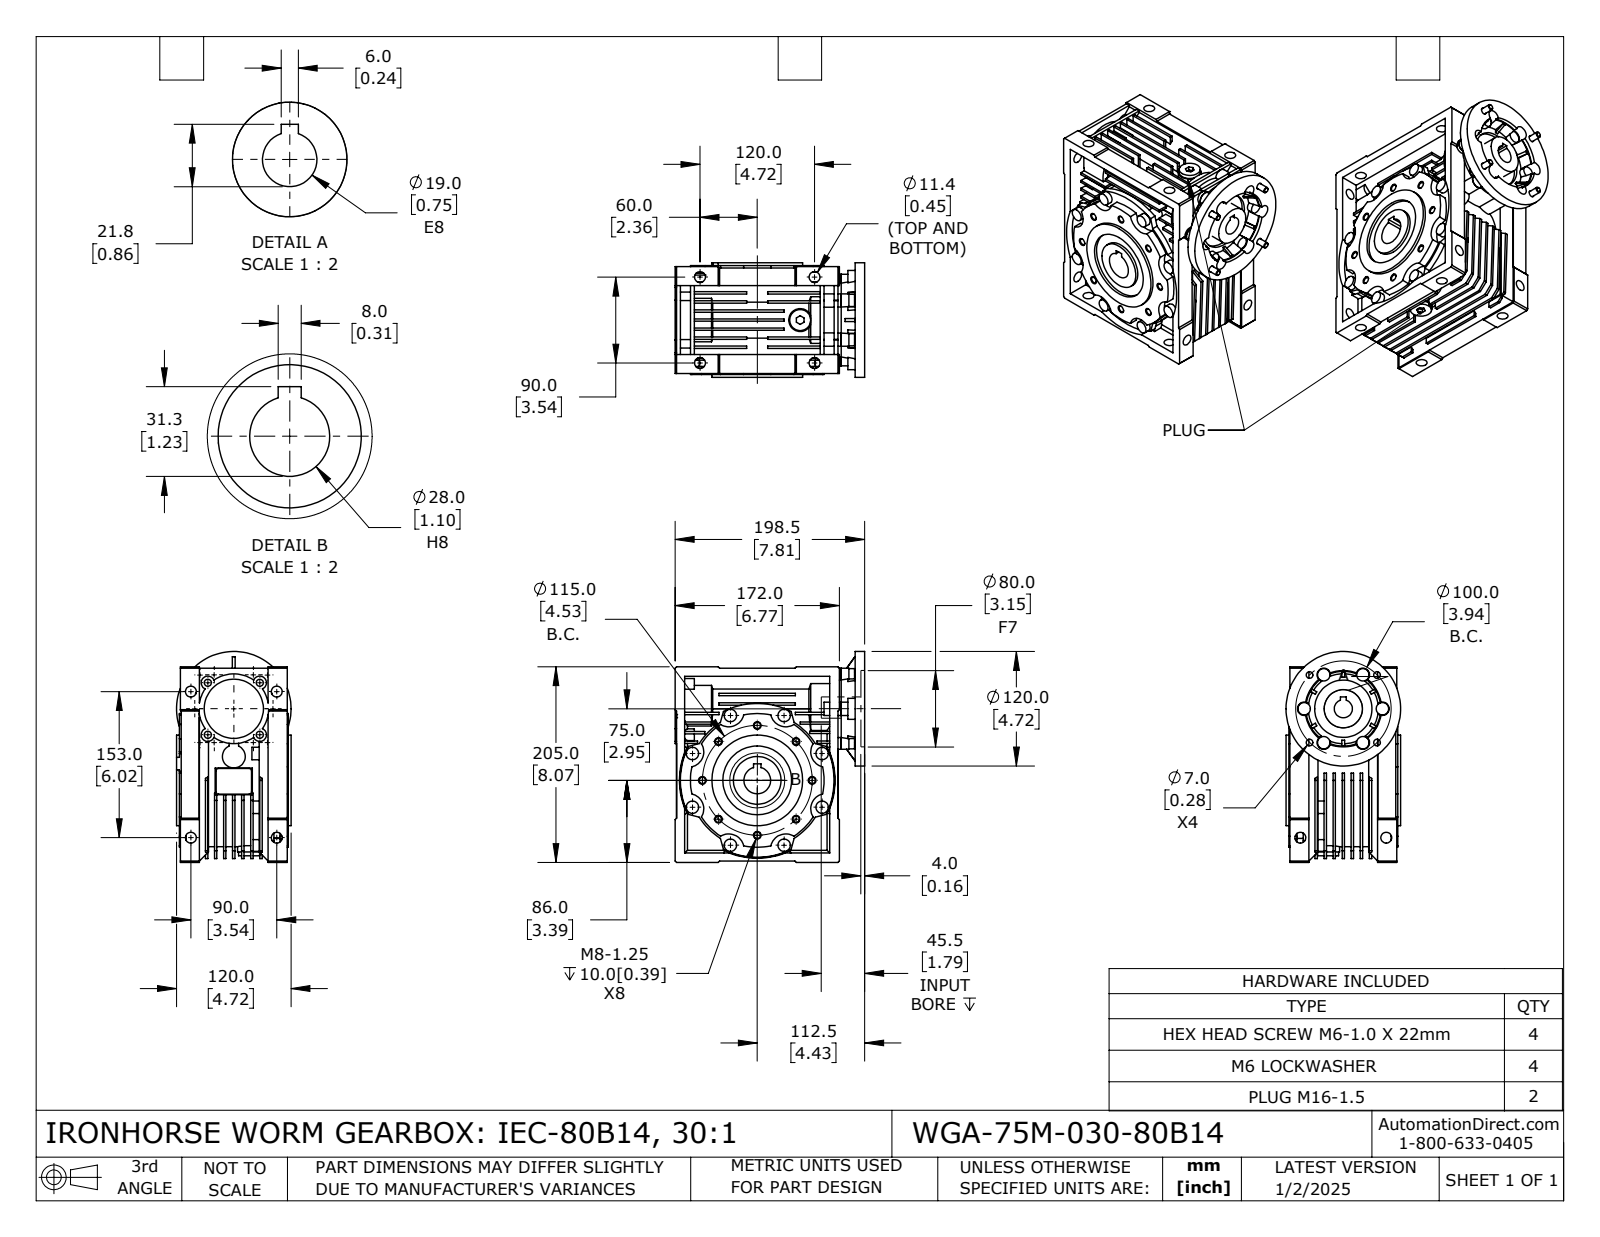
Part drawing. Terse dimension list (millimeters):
name: WGA-75M-030-80B14
written by: SolidWorks 2024 (CONFIG_CONTROL_DESIGN)
unit: mm
bodies: 16 solids, 1304 faces (703 planar, 433 cylindrical, 168 other)
size: 221 × 209 × 120
volume: 2 853 000 mm³; area: 480 911 mm²
holes: 8× ⌀6.65, 8× ⌀11.38, 4× ⌀6.1, 4× ⌀7, 4× ⌀7.45, 2× ⌀14.5, 1× ⌀19, 1× ⌀20, 1× ⌀28, 1× ⌀39, 1× ⌀42, 1× ⌀50
bosses: 14× ⌀13, 4× ⌀12.2, 4× ⌀6, 3× ⌀24, 2× ⌀22, 2× ⌀15.8, 2× ⌀13.7, 1× ⌀139.93
rounds: 10× R7, 8× R16, 6× R11, 4× R2.5, 1× R36, 1× R36.5, 1× R39, 1× R40
face distances: 9.5, 2.5, 19, 12, 10, 7, 16.5, 28.5, 27.75, 21.5
hole spacings: 44.01, 57.5, 63.11, 81.32, 106.25, 11.51, 38.49, 50.01
